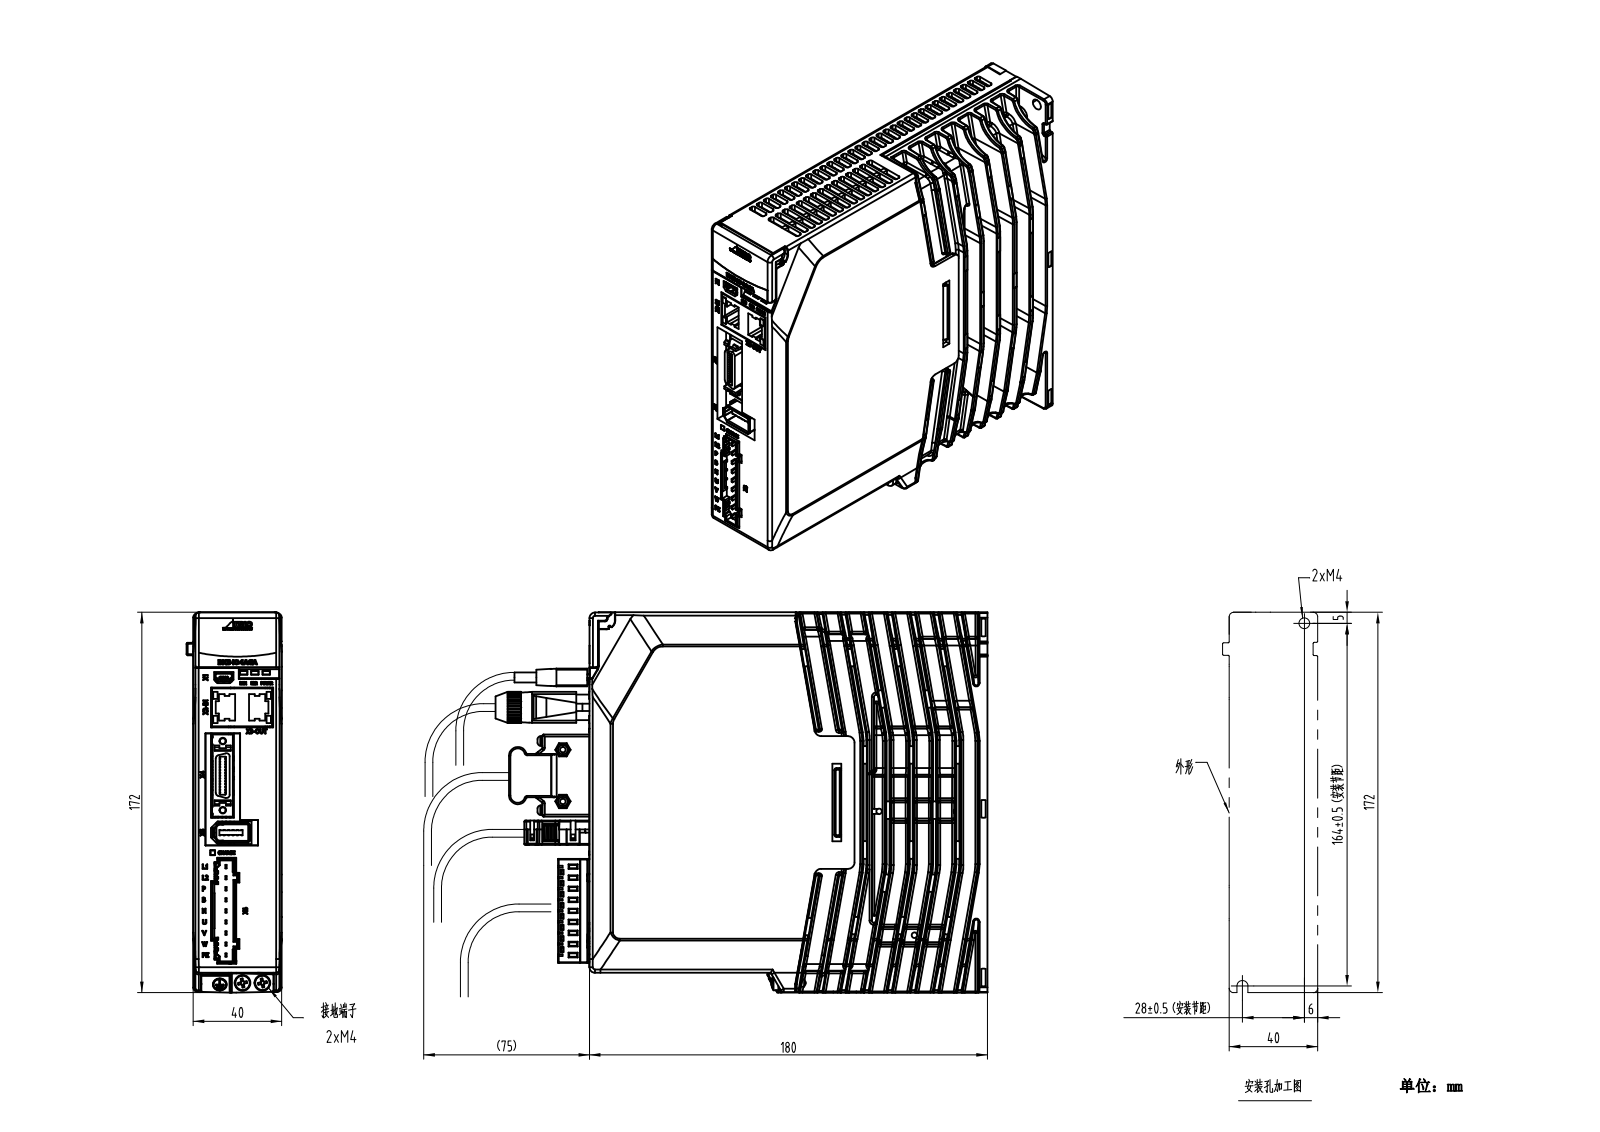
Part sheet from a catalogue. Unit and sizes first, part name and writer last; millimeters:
Units: millimetres
Overall size (bounding box): 181 × 172 × 43
Round holes (diameter × count): ⌀2 ×7, ⌀2.5 ×7, ⌀3.5 ×7, ⌀3.2 ×6, ⌀3.4 ×6, ⌀1.2 ×3, ⌀2.2 ×3, ⌀8 ×3, ⌀1.25 ×2, ⌀2.05 ×2, ⌀2.6 ×2, ⌀2.8 ×2
Round bosses / shafts (diameter × count): ⌀1 ×16, ⌀0.5 ×10, ⌀7 ×6, ⌀5.6 ×6, ⌀5 ×6, ⌀4 ×6, ⌀3 ×6, ⌀2.3 ×4
Partial cylindrical surfaces — rounded edges, fillets, slot ends (radius × count): R1 ×287, R0.5 ×282, R0.3 ×146, R0.15 ×103, R0.2 ×76, R1.5 ×27, R4 ×26, R0.9 ×21
Main face-to-face distances: 2, 8.5, 6.5, 31.5, 33.5, 40, 10.5, 23, 8.3, 6.3
Hole centre spacings: 9.12, 34.69, 6.5, 148, 4.74, 5, 6.14, 12.36
Volume: 345 582 mm³ · Surface area: 284 734 mm²
Bodies: 45 solids, 10034 faces (6148 planar, 1900 cylindrical, 1986 other)
STEP written by: SolidWorks 2018 (CONFIG_CONTROL_DESIGN)
